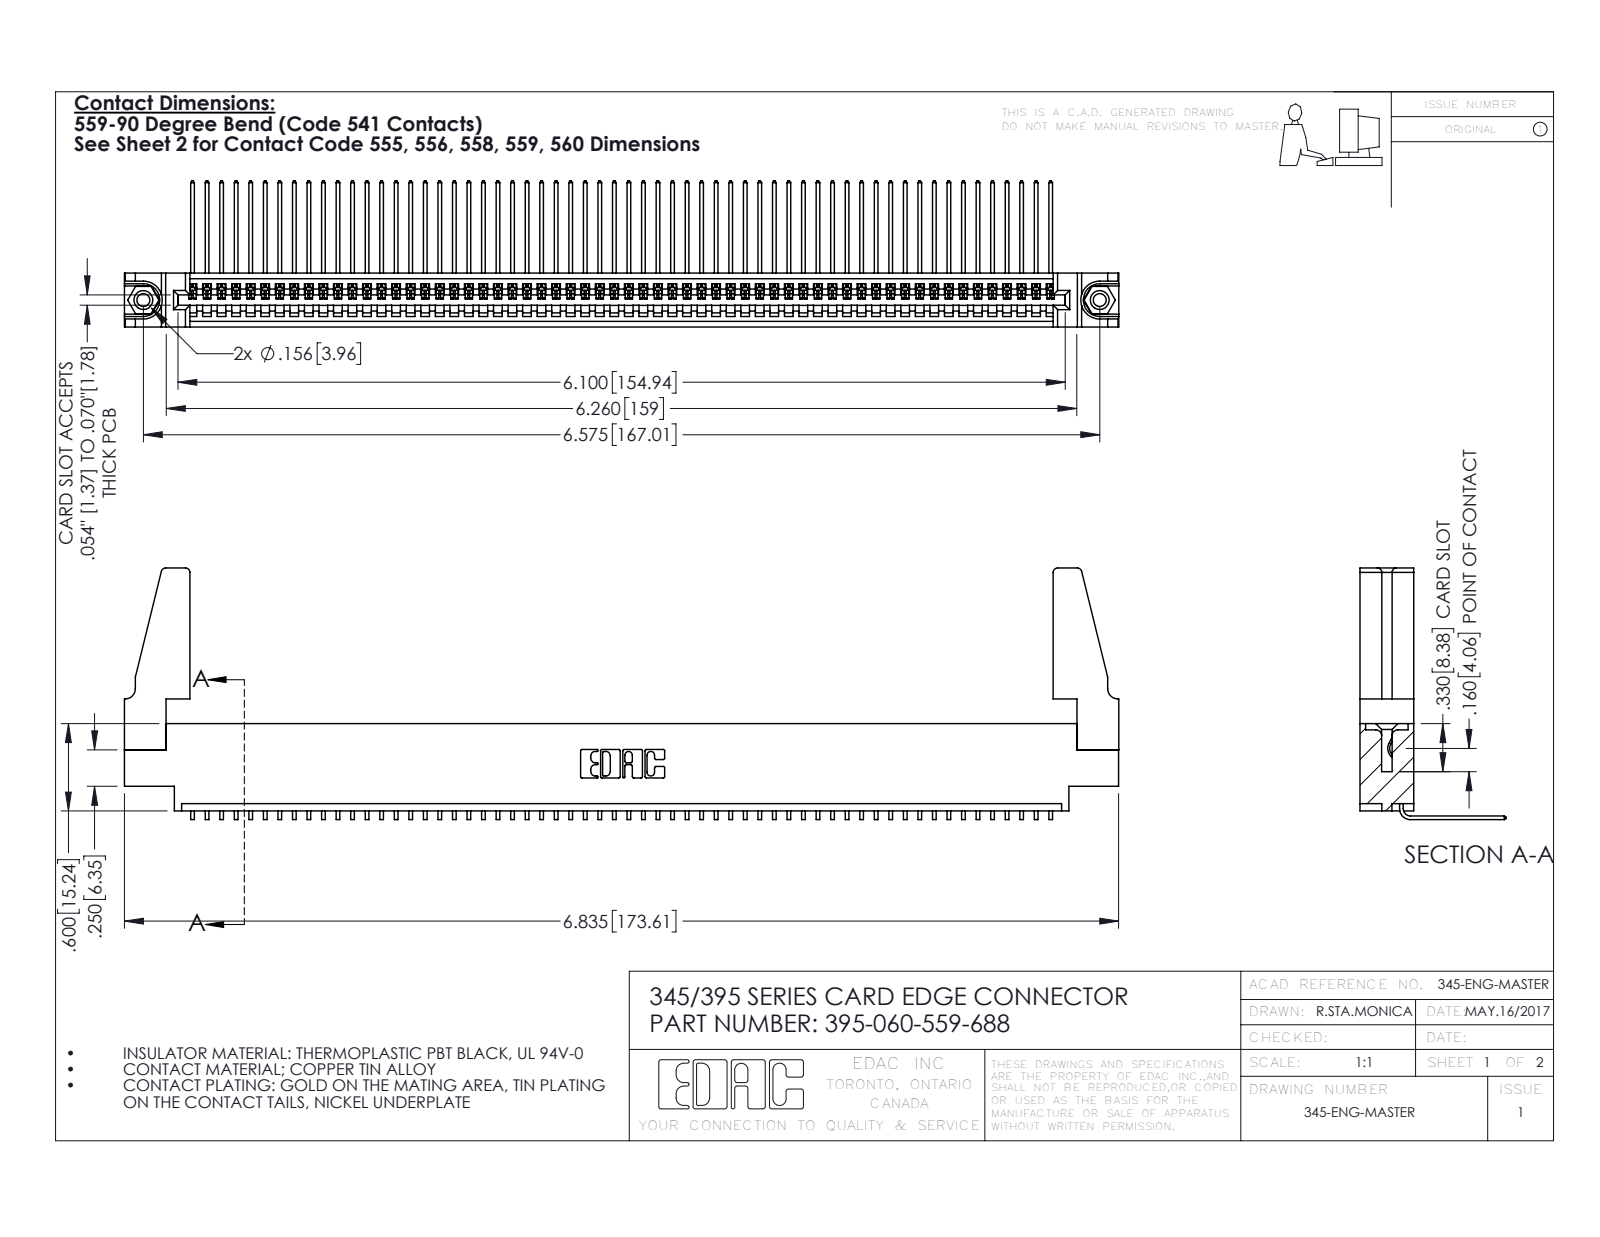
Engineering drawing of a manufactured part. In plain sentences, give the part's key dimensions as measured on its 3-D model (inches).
The part is named "345 Part_0.170 Offset - 0.156 Dia-TH; 345-220-078_345-220-088; 395-060-559-688; 345-250-001_345-250-001-102 (+1 more)". Its 3-D file was written by "SolidWorks 2016 (CONFIG_CONTROL_DESIGN)". It is 65 solids with 3854 faces: 2676 planar, 1162 cylindrical and 16 other. Overall it measures 6.836 by 1.729 by 1.005 inches. Its volume is 1.219 cubic inches and its surface area 41.7 square inches. Round holes: 2 of diameter 0.089, 2 of diameter 0.125, 2 of diameter 0.156, 1 of diameter 0.064. Round bosses or shafts: 2 of diameter 0.155. Partial cylindrical surfaces (rounded edges, fillets, slot ends): 120 of radius 0.006, 22 of radius 0.01, 8 of radius 0.03, 6 of radius 0.007, 6 of radius 0.031, 3 of radius 0.026, 2 of radius 0.031, 2 of radius 0.04. The main face-to-face distances are 0.072, 0.298, 0.37, 0.098, 0.272, 0.025, 0.2, 0.225, 0.175, 0.149. The hole center spacings are 0.27, 6.339, 6.575.
